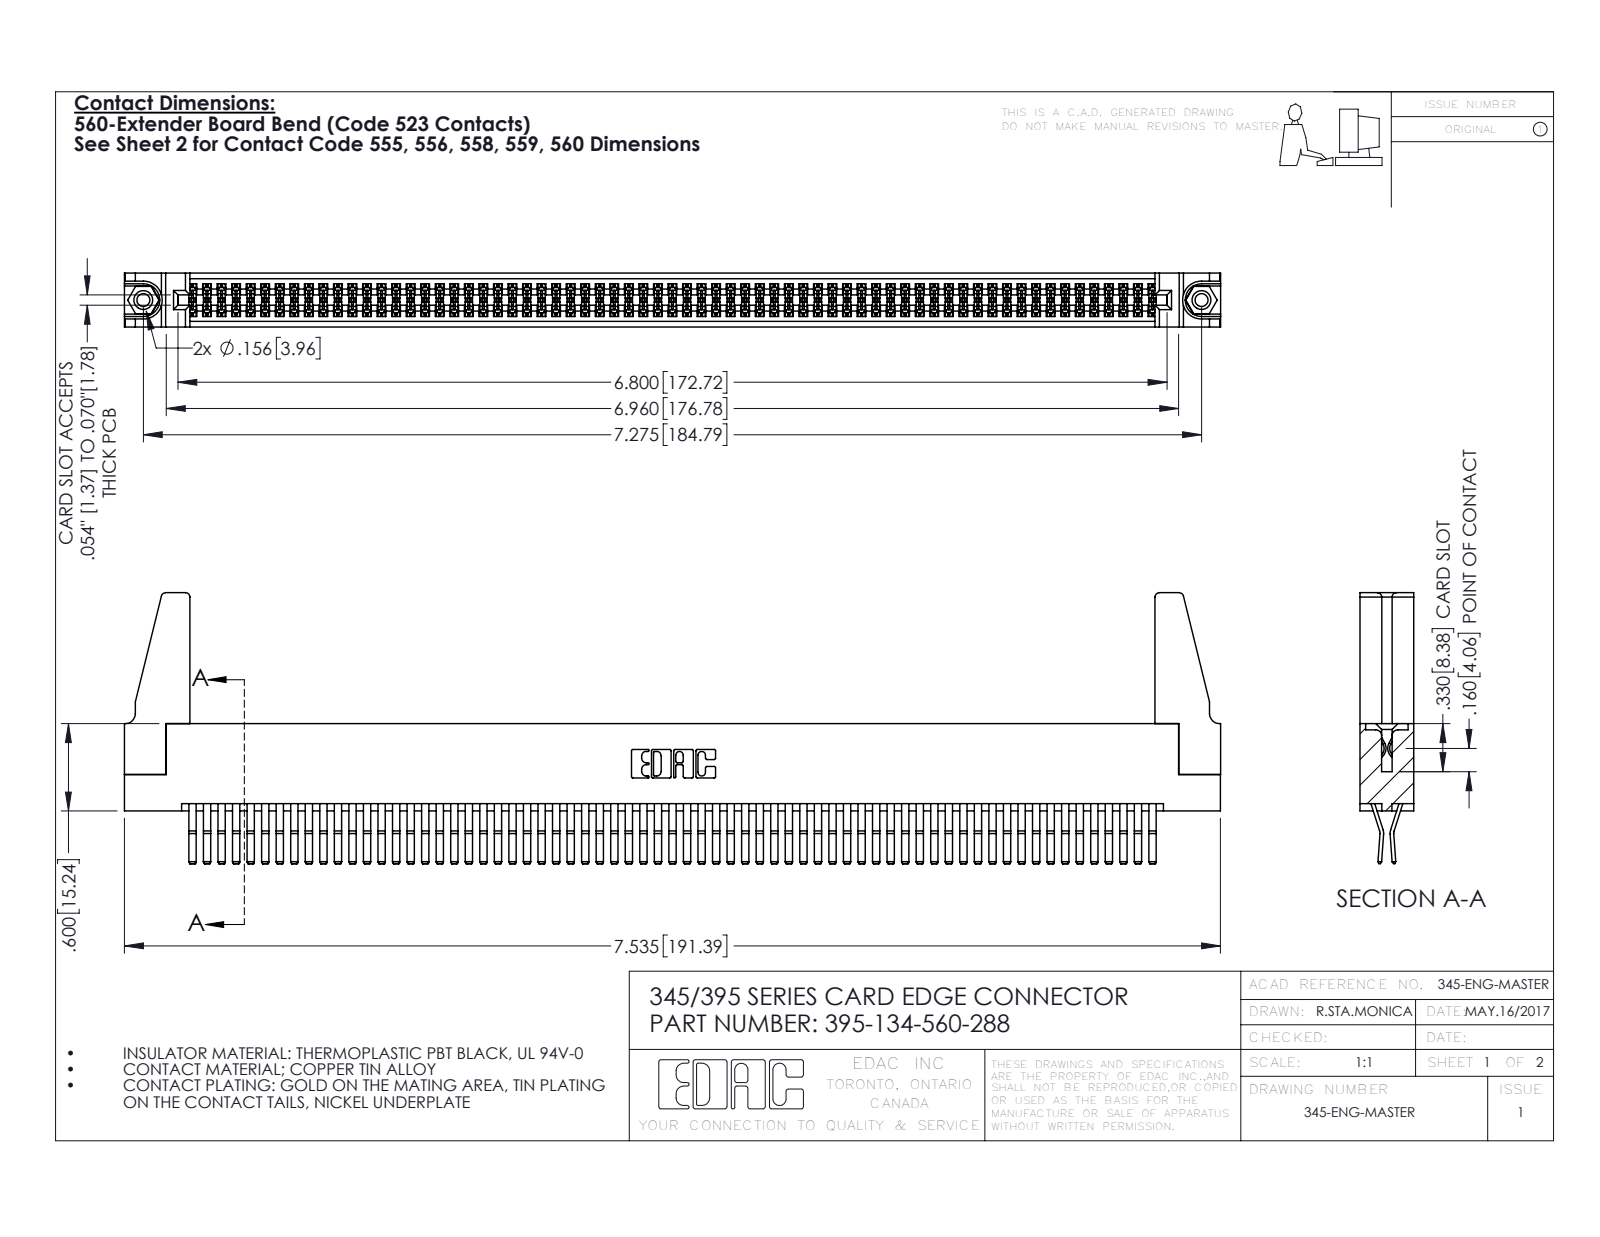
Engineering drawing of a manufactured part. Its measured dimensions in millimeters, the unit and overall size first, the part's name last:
Units: millimetres
Overall size (bounding box): 191.4 × 47.3 × 9.4
Round holes (diameter × count): ⌀2.3 ×2, ⌀3.2 ×2, ⌀4 ×2, ⌀1.6 ×1
Round bosses / shafts (diameter × count): ⌀3.9 ×2
Partial cylindrical surfaces — rounded edges, fillets, slot ends (radius × count): R0.2 ×201, R0.3 ×22, R0.8 ×8, R0.2 ×6, R0.8 ×6, R0.7 ×3, R0.3 ×2, R0.4 ×2
Main face-to-face distances: 1.8, 0.6, 7.6, 9.4, 5.1, 2.5, 6.9, 5.7, 4.4, 3.8
Hole centre spacings: 6.9, 178.8, 184.8
Volume: 22 960 mm³ · Surface area: 34 990 mm²
Bodies: 139 solids, 7218 faces (4574 planar, 2628 cylindrical, 16 other)
Part name (STEP PRODUCT): 345-220-078_345-220-088; 345 Part_Flush Mounting Lugs - 0.156 Dia-TH; 345-250-001_345-250-001-102; 395-134-560-288 (+1 more)
STEP written by: SolidWorks 2016 (CONFIG_CONTROL_DESIGN)
